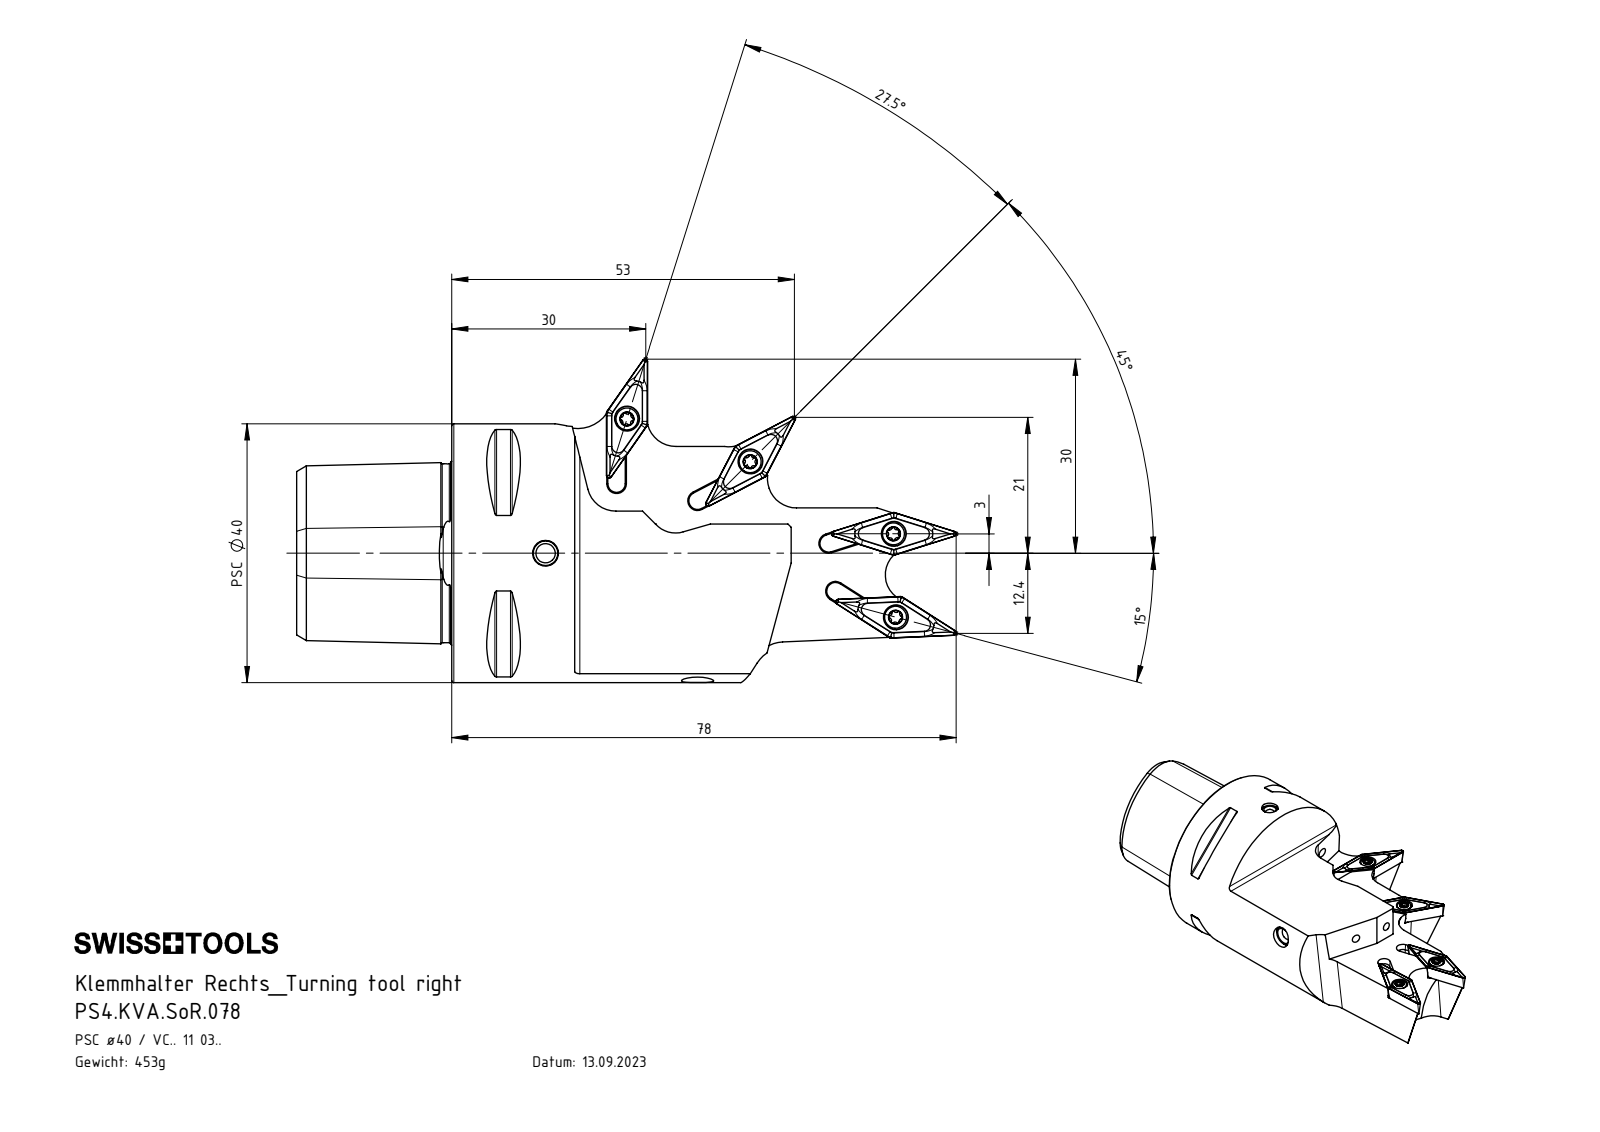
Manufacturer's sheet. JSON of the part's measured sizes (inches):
{"part_name": "PS4.KVA.SoR.078; VCGT110304; KVT_MB_600_040; PS4-KVA.SoR.078_A_Fertigbearbeitung (+2 more)", "step_written_by": "SolidWorks 2017 (AUTOMOTIVE_DESIGN)", "units": "inches", "bodies": {"solids": 13, "faces": 658, "planar": 163, "cylindrical": 175, "other": 320}, "overall_size": [4.016, 1.969, 1.575], "volume_in3": 3.488, "surface_area_in2": 26.46, "round_holes": [[0.079, 4], [0.081, 4], [0.11, 4], [0.152, 4], [0.157, 2], [0.118, 1], [0.13, 1], [0.165, 1], [0.181, 1], [0.197, 1], [0.492, 1], [0.709, 1]], "round_bosses_or_shafts": [[0.134, 4], [0.098, 4], [1.575, 1], [0.197, 1], [0.157, 1]], "partial_cylinders_radius": [[0.008, 24], [0.014, 16], [0.012, 8], [0.014, 8], [0.053, 4], [0.177, 4], [0.031, 2], [0.167, 2]], "face_to_face_distances": [0.878, 0.579, 0.299, 0.465, 0.113, 0.413, 0.748, 0.945, 1.693, 0.591], "hole_center_spacings": [0.507, 1.296, 1.298, 0.098, 0.508, 0.509, 0.794, 0.794]}
